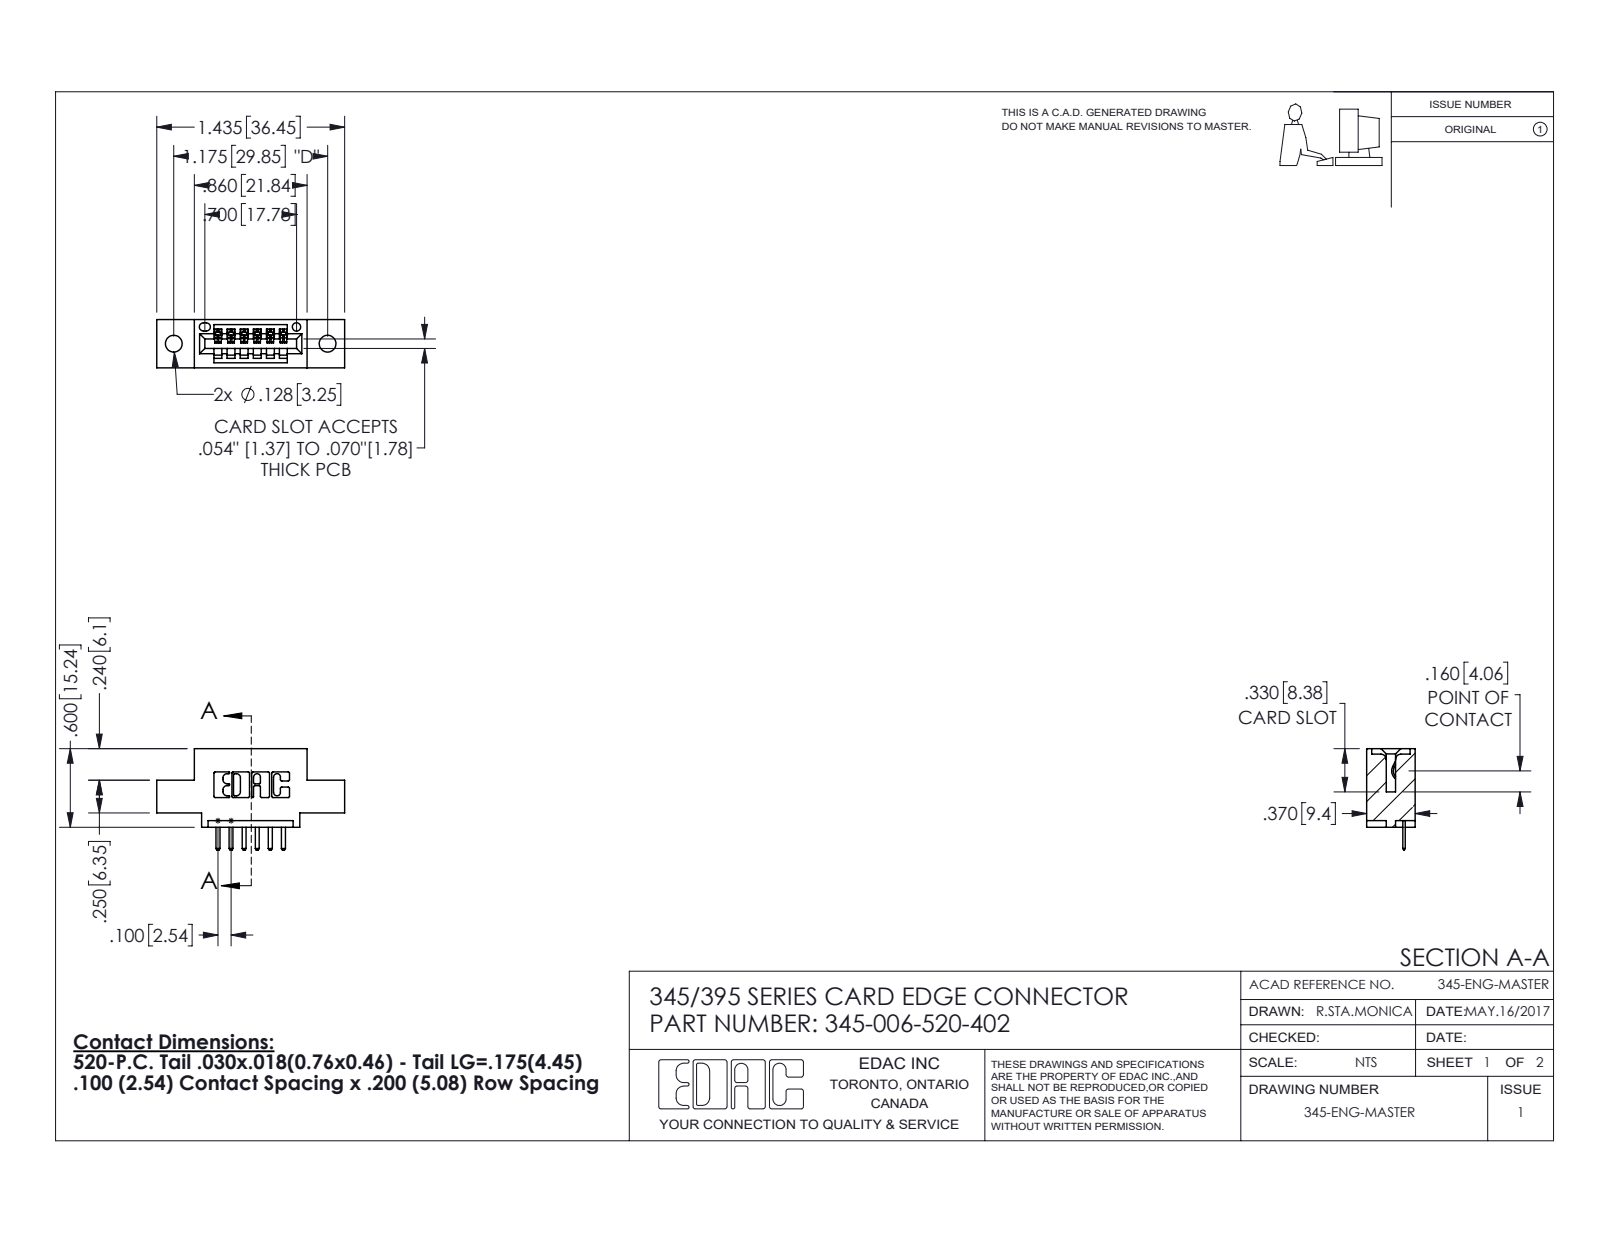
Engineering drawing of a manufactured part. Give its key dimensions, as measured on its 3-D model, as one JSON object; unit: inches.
{"part_name": "345 Part_0.110 Offset - 0.128 Dia; 345-292-001_345-293-120; 345-006-520-402", "step_written_by": "SolidWorks 2016 (CONFIG_CONTROL_DESIGN)", "units": "inches", "bodies": {"solids": 7, "faces": 502, "planar": 336, "cylindrical": 166, "other": 0}, "overall_size": [1.435, 0.775, 0.37], "volume_in3": 0.185, "surface_area_in2": 5.122, "round_holes": [[0.128, 2], [0.064, 1]], "partial_cylinders_radius": [[0.01, 22], [0.01, 14], [0.006, 12], [0.007, 6], [0.031, 6], [0.026, 3], [0.031, 2], [0.04, 2]], "face_to_face_distances": [0.2, 0.37, 0.1, 0.298, 0.072, 0.16, 0.06, 0.3, 0.25, 0.025], "hole_center_spacings": [0.27, 0.946, 1.175]}
